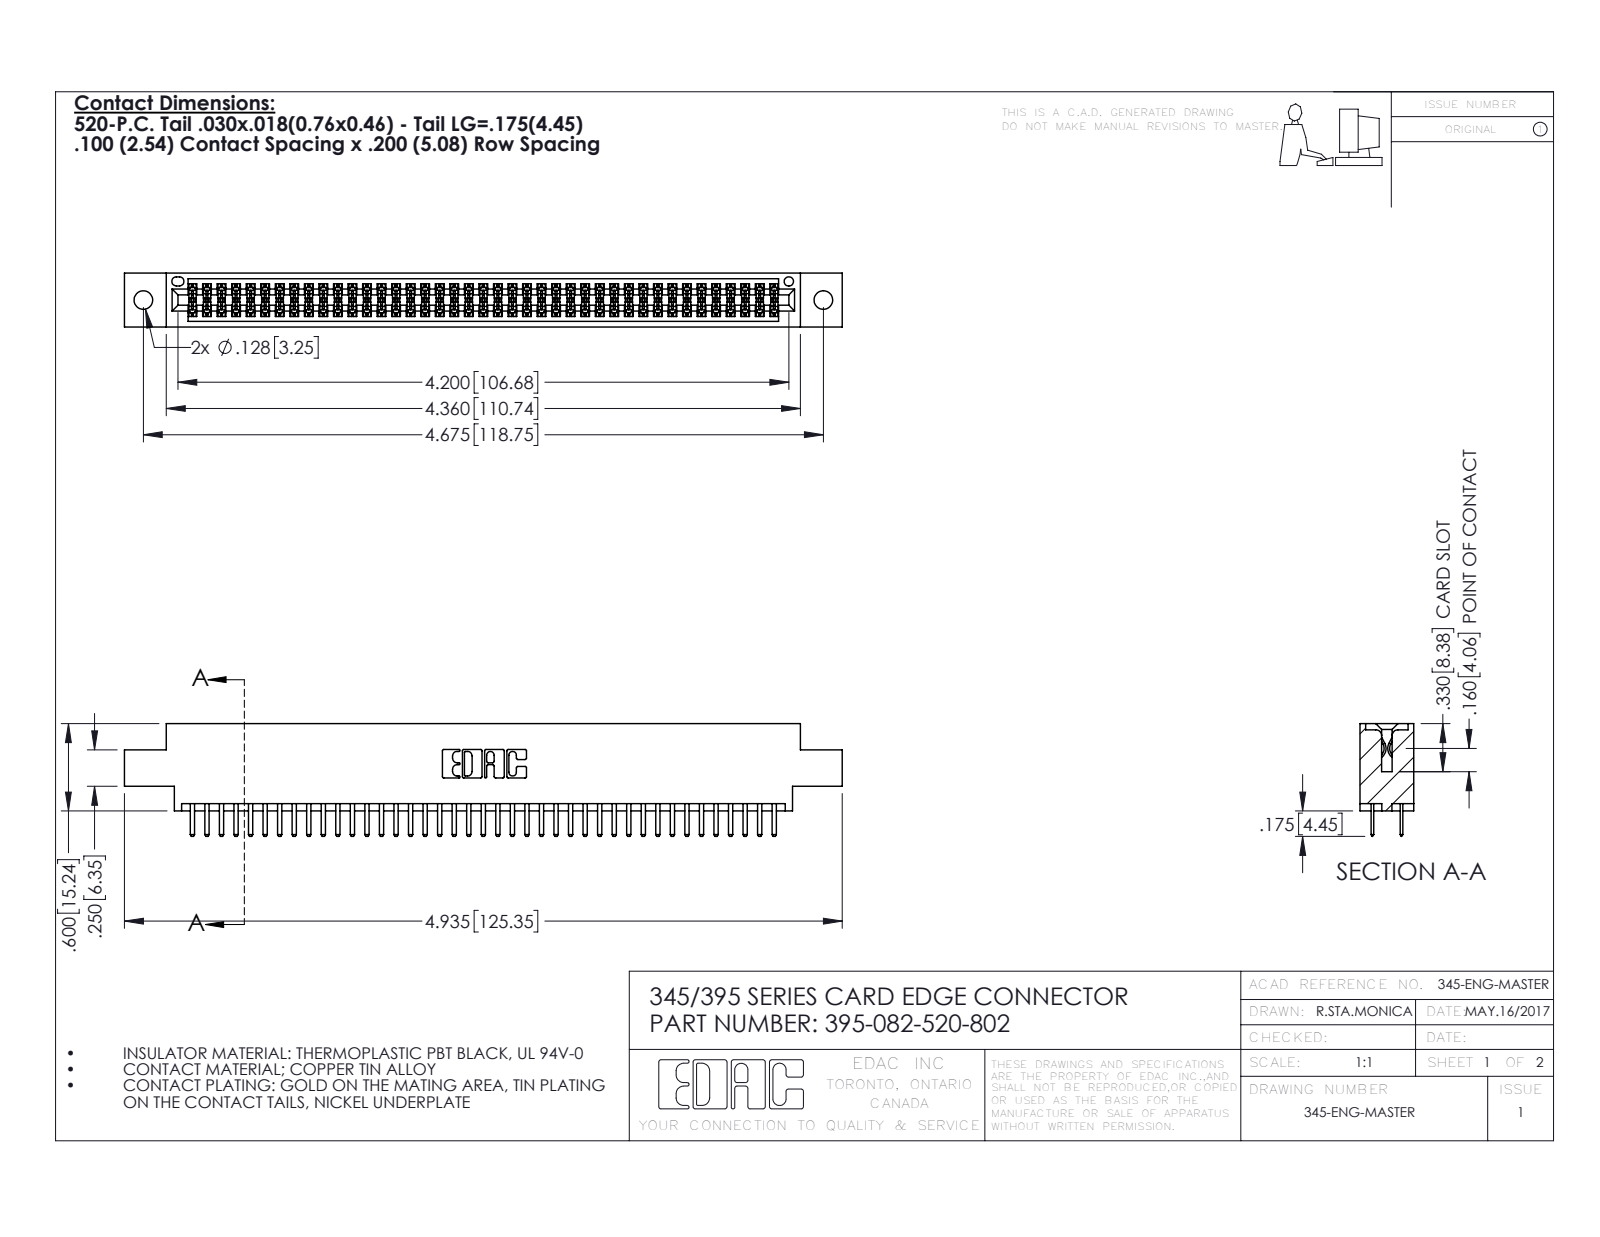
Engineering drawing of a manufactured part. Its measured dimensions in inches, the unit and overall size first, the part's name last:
Units: inches
Overall size (bounding box): 4.935 × 0.775 × 0.37
Round holes (diameter × count): ⌀0.128 ×2, ⌀0.064 ×1
Partial cylindrical surfaces — rounded edges, fillets, slot ends (radius × count): R0.006 ×123, R0.01 ×86, R0.01 ×22, R0.007 ×6, R0.031 ×6, R0.026 ×3, R0.014 ×2, R0.019 ×2
Main face-to-face distances: 0.298, 0.072, 0.2, 0.37, 0.098, 0.272, 0.025, 0.225, 0.022, 0.175
Hole centre spacings: 0.27, 4.439, 4.675
Volume: 0.731 in³ · Surface area: 27.1 in²
Bodies: 83 solids, 4558 faces (2954 planar, 1604 cylindrical, 0 other)
Part name (STEP PRODUCT): 395-082-520-802; 345 Part_0.170 Offset - 0.128 Dia; 345-292-001_345-293-120
STEP written by: SolidWorks 2016 (CONFIG_CONTROL_DESIGN)
